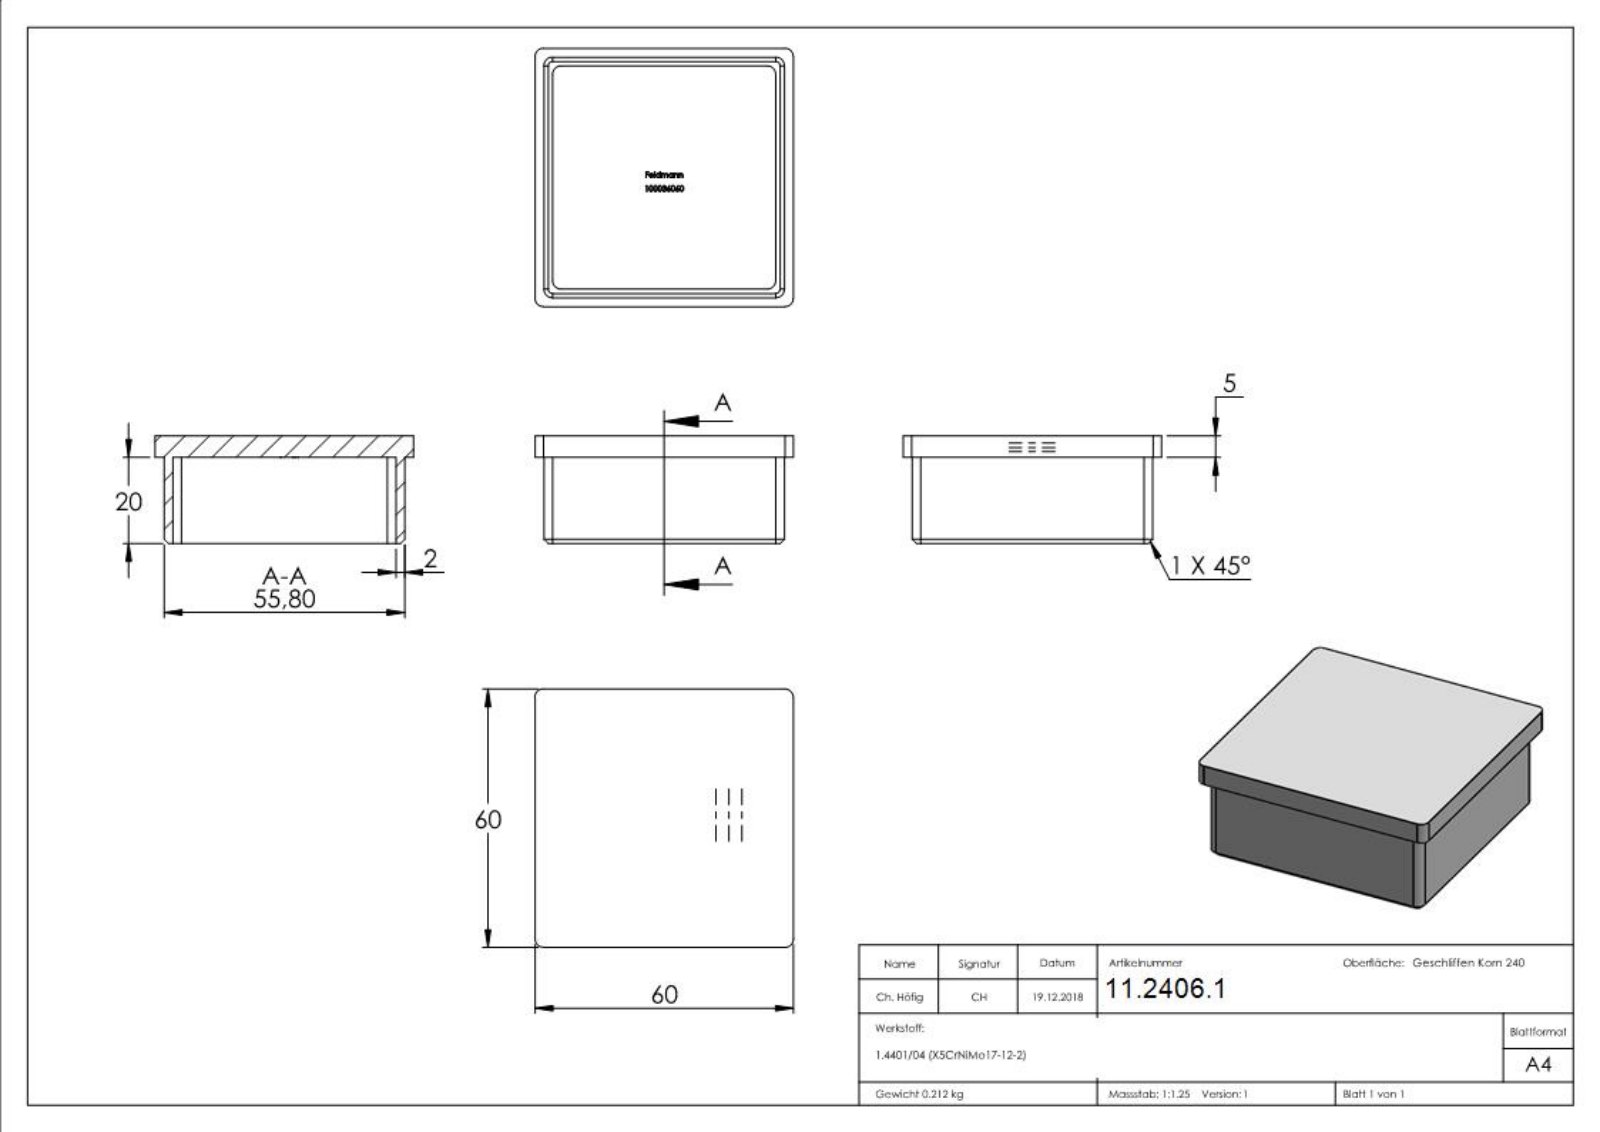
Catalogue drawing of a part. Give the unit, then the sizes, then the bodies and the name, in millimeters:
Units: millimetres
Overall size (bounding box): 60 × 60 × 25
Partial cylindrical surfaces — rounded edges, fillets, slot ends (radius × count): R2 ×12
Main face-to-face distances: 2, 53.8, 5, 55.8, 51.8, 2.1, 4.1, 55.9, 57.9, 60
Volume: 26 481 mm³ · Surface area: 16 727 mm²
Bodies: 1 solid, 257 faces (116 planar, 12 cylindrical, 129 other)
Part name (STEP PRODUCT): 100036060
STEP written by: SolidWorks 2015 (CONFIG_CONTROL_DESIGN)
